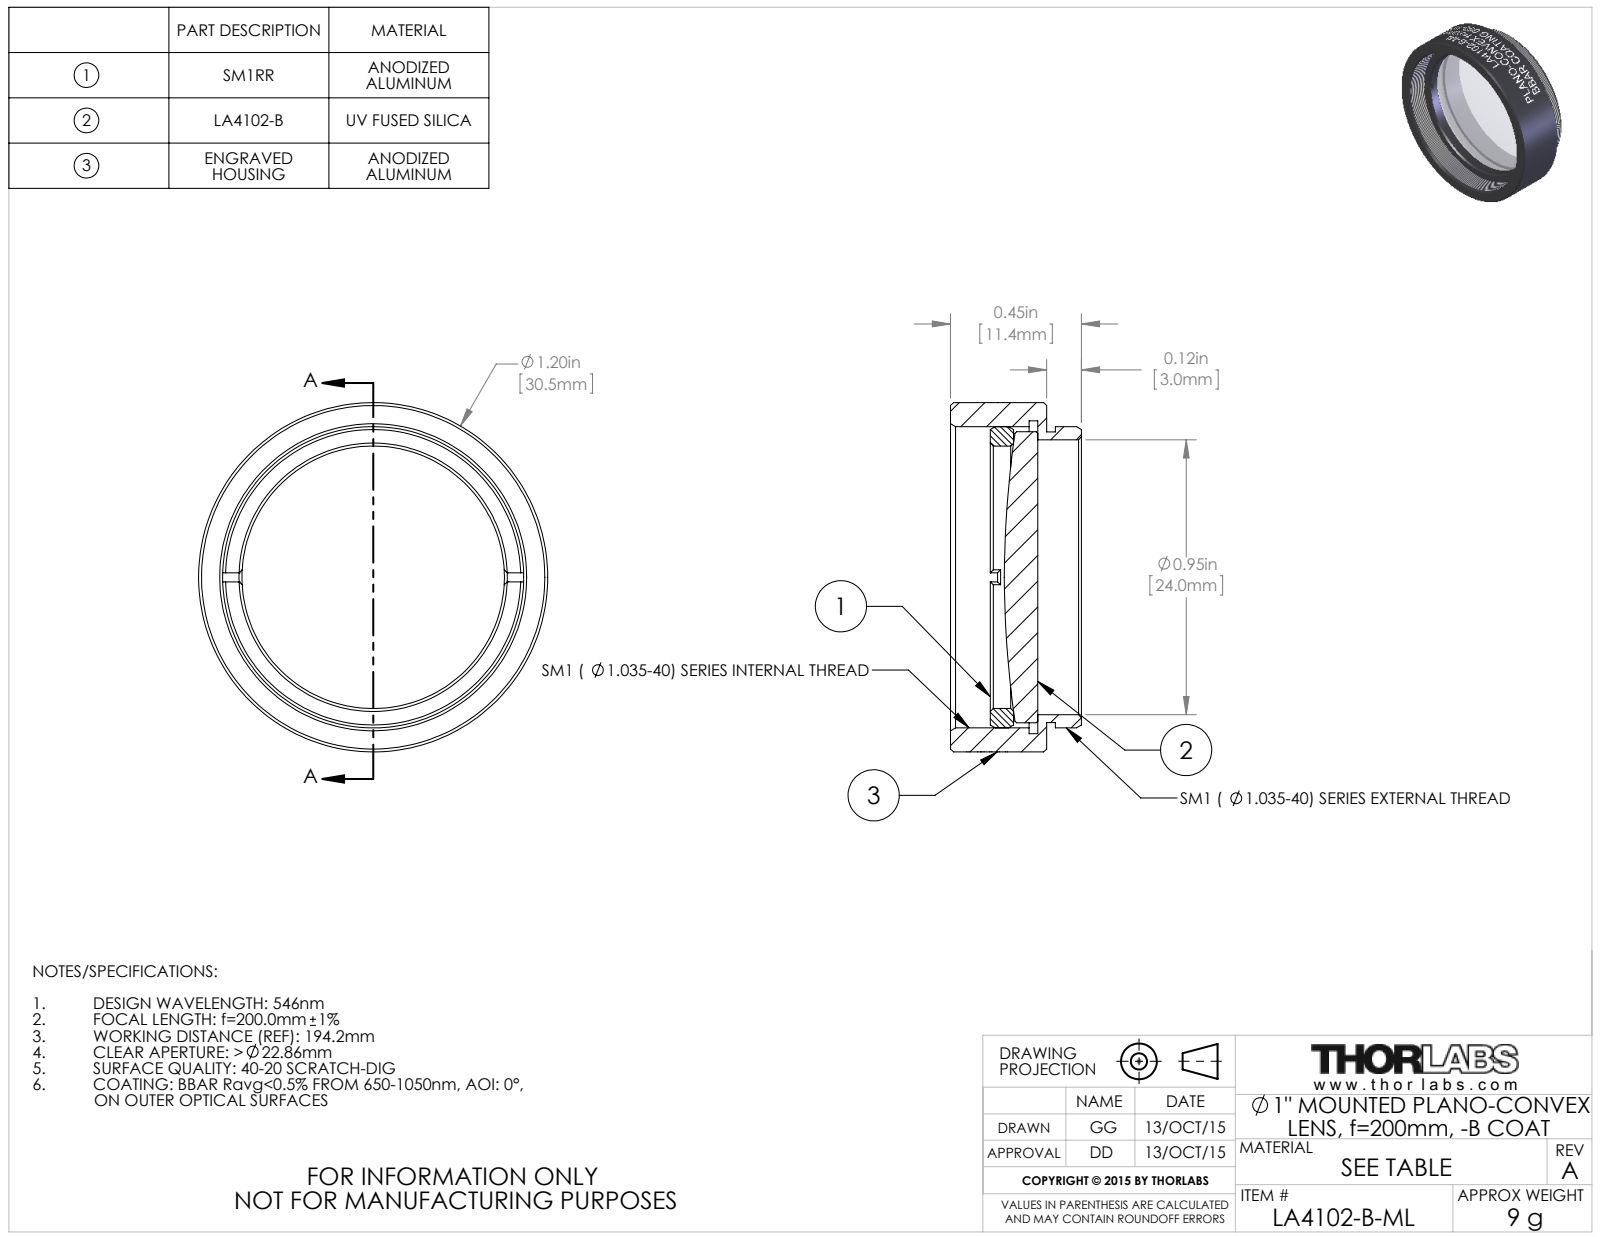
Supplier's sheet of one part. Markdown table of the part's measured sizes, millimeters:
| quantity | value |
| --- | --- |
| part name | TTN039147-E0W |
| STEP written by | SolidWorks 2014 (CONFIG_CONTROL_DESIGN) |
| units | millimeters |
| bodies | 3 solids, 158 faces (20 planar, 110 cylindrical, 28 other) |
| overall size | 30.48 × 30.48 × 11.43 |
| volume | 3 318 mm³ |
| surface area | 4 302 mm² |
| round holes (diameter × count) | 22.91 × 1, 24 × 1, 26.29 × 1, 27.3 × 1 |
| round bosses / shafts (diameter × count) | 30.48 × 1, 26.29 × 1, 25.4 × 1, 25.37 × 1 |
| main face-to-face distances | 0.76, 8.38, 7.62, 2.88, 2.12, 5.5, 4.91, 4.15, 2.03, 3.47 |
